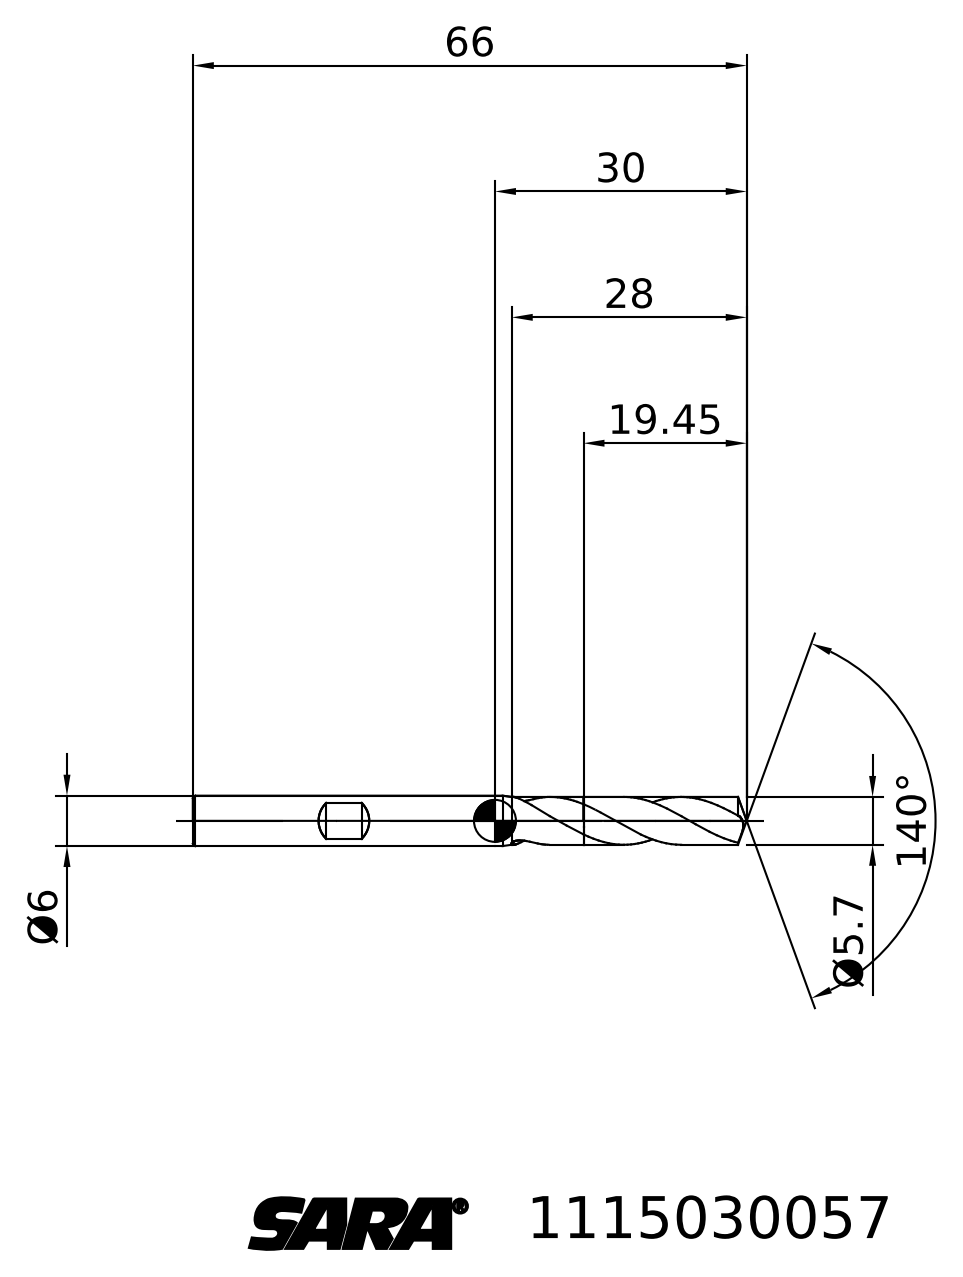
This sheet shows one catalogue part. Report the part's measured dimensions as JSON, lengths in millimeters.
{"step_written_by": "TDM (AUTOMOTIVE_DESIGN)", "units": "millimeters", "bodies": {"solids": 2, "faces": 27, "planar": 3, "cylindrical": 0, "other": 24}, "overall_size": [66, 6, 6], "volume_mm3": 1545, "surface_area_mm2": 1321, "face_to_face_distances": [46.55]}
